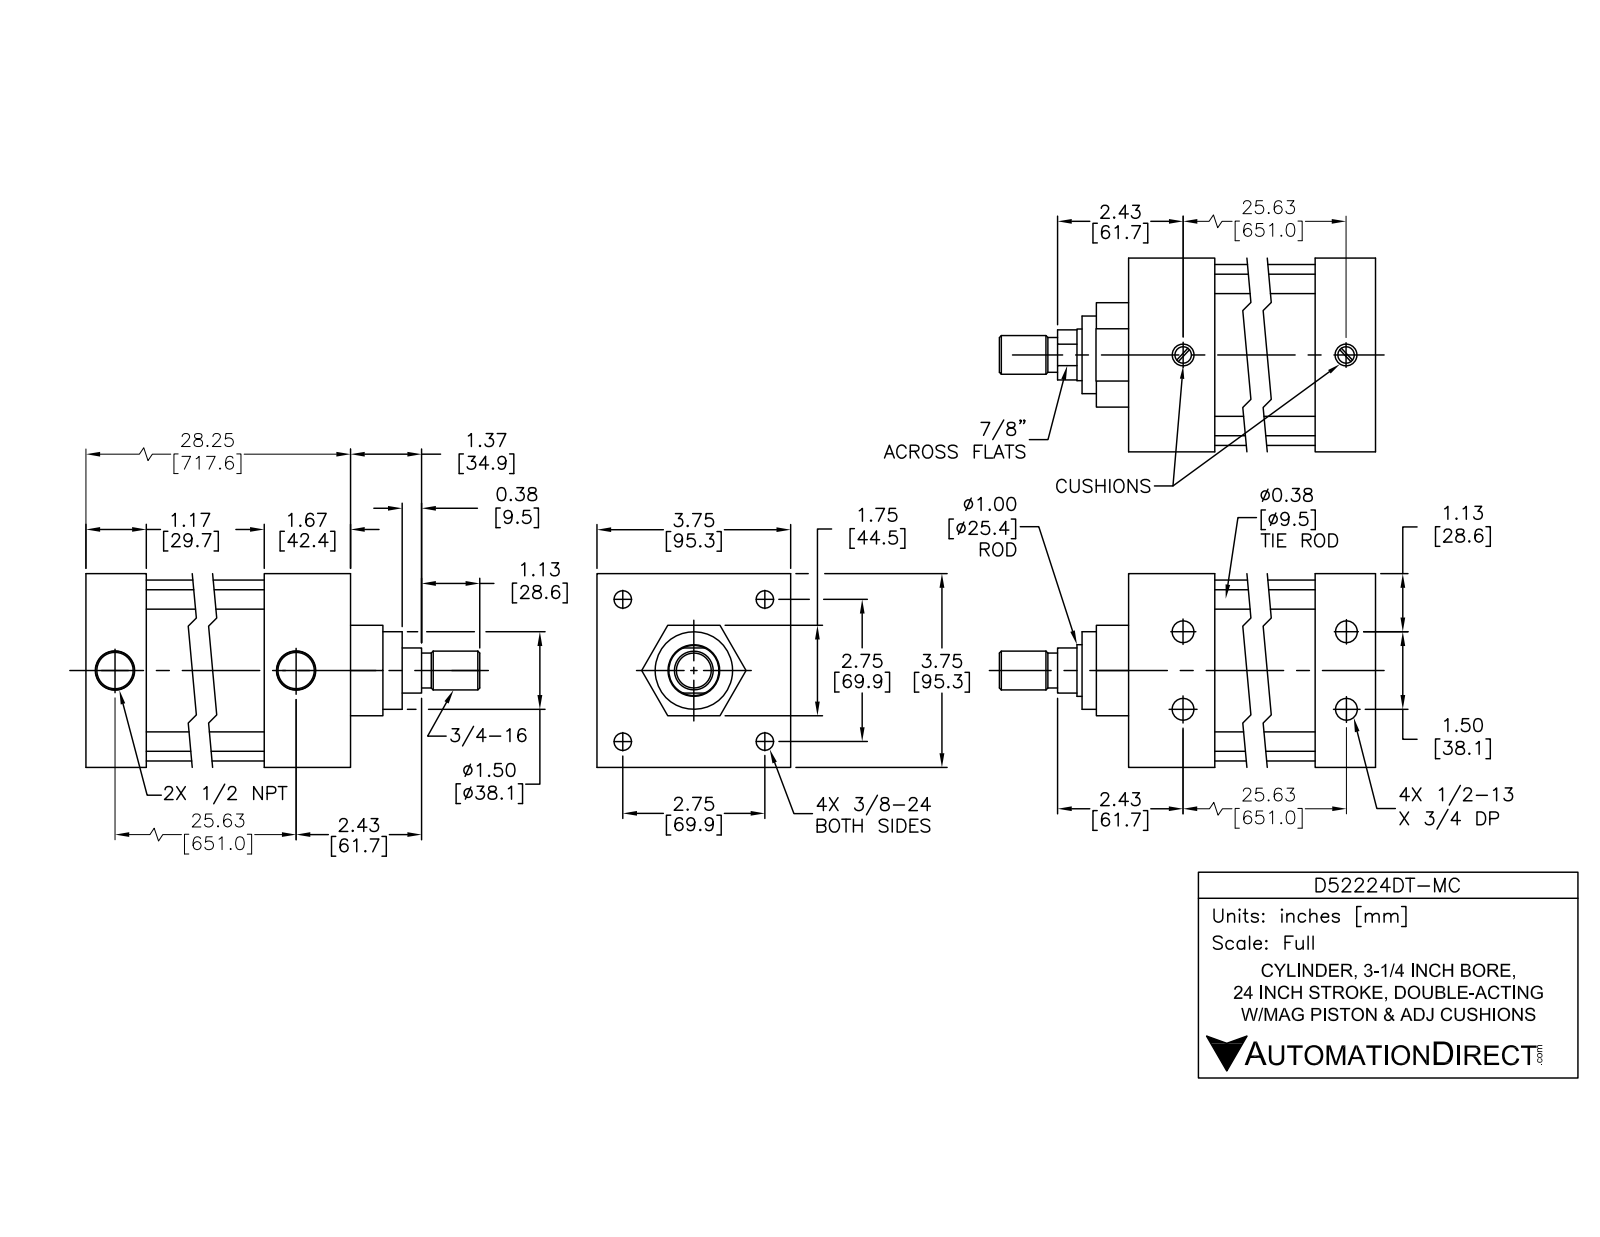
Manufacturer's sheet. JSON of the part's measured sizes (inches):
{"part_name": "D52240DT-MC; D52240DT-M BODY; D52240DT-M PISTON", "step_written_by": "SolidWorks 2015 (AUTOMOTIVE_DESIGN)", "units": "inches", "bodies": {"solids": 12, "faces": 303, "planar": 99, "cylindrical": 114, "other": 90}, "overall_size": [30.745, 3.75, 3.75], "volume_in3": 113.1, "surface_area_in2": 923.7, "round_holes": [[0.33, 4], [0.406, 4], [0.417, 4], [0.625, 4], [0.5, 2], [0.766, 2], [1, 1], [1.003, 1], [3.25, 1]], "round_bosses_or_shafts": [[0.609, 4], [0.375, 4], [0.34, 4], [3.5, 1], [3.247, 1], [1.75, 1], [0.997, 1], [0.97, 1]], "partial_cylinders_radius": [[0.375, 4]], "face_to_face_distances": [3.75, 0.08, 25.326, 28.246, 1.75, 26.997, 1.249, 25.751, 1.246, 2.495], "hole_center_spacings": [2.758, 1.95, 0.75, 0.76, 1.5, 3.9, 26.5, 26.515]}
